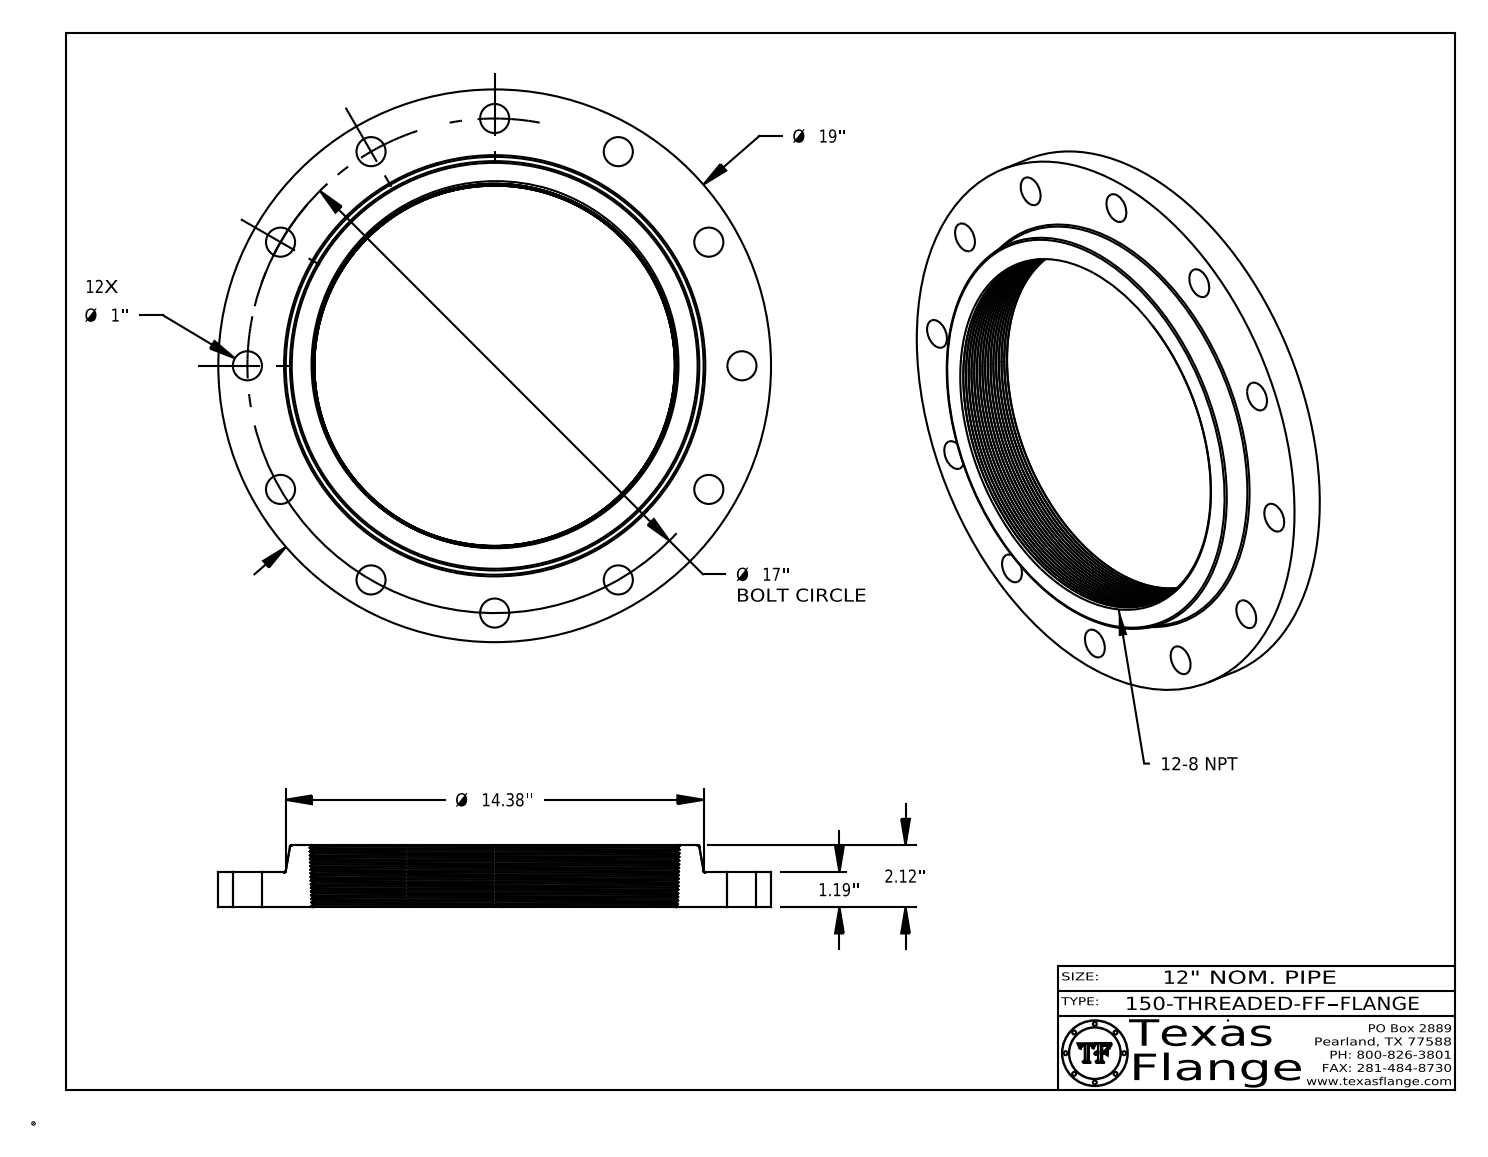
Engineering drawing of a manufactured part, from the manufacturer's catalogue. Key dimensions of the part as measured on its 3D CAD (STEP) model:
Part name (STEP PRODUCT): 150-THREADED-FF
STEP written by: CATIA V5 STEP AP214 (AUTOMOTIVE_DESIGN)
Units: inches
Bodies: 1 solid, 597 faces (368 planar, 46 cylindrical, 183 other)
Overall size (bounding box): 19 × 19 × 2.12
Volume: 211.7 in³ · Surface area: 607 in²
Round holes (diameter × count): ⌀1 ×12, ⌀0.495 ×1
Round bosses / shafts (diameter × count): ⌀0.03 ×8, ⌀19 ×1, ⌀0.39 ×1
Main face-to-face distances: 1.19, 2.12, 0.93, 0.015, 1.175, 0.945, 0.148, 0.145, 0.027, 0.122
Hole centre spacings: 8.5, 16.42, 4.4, 12.02, 14.722, 4.4, 12.021, 14.722
